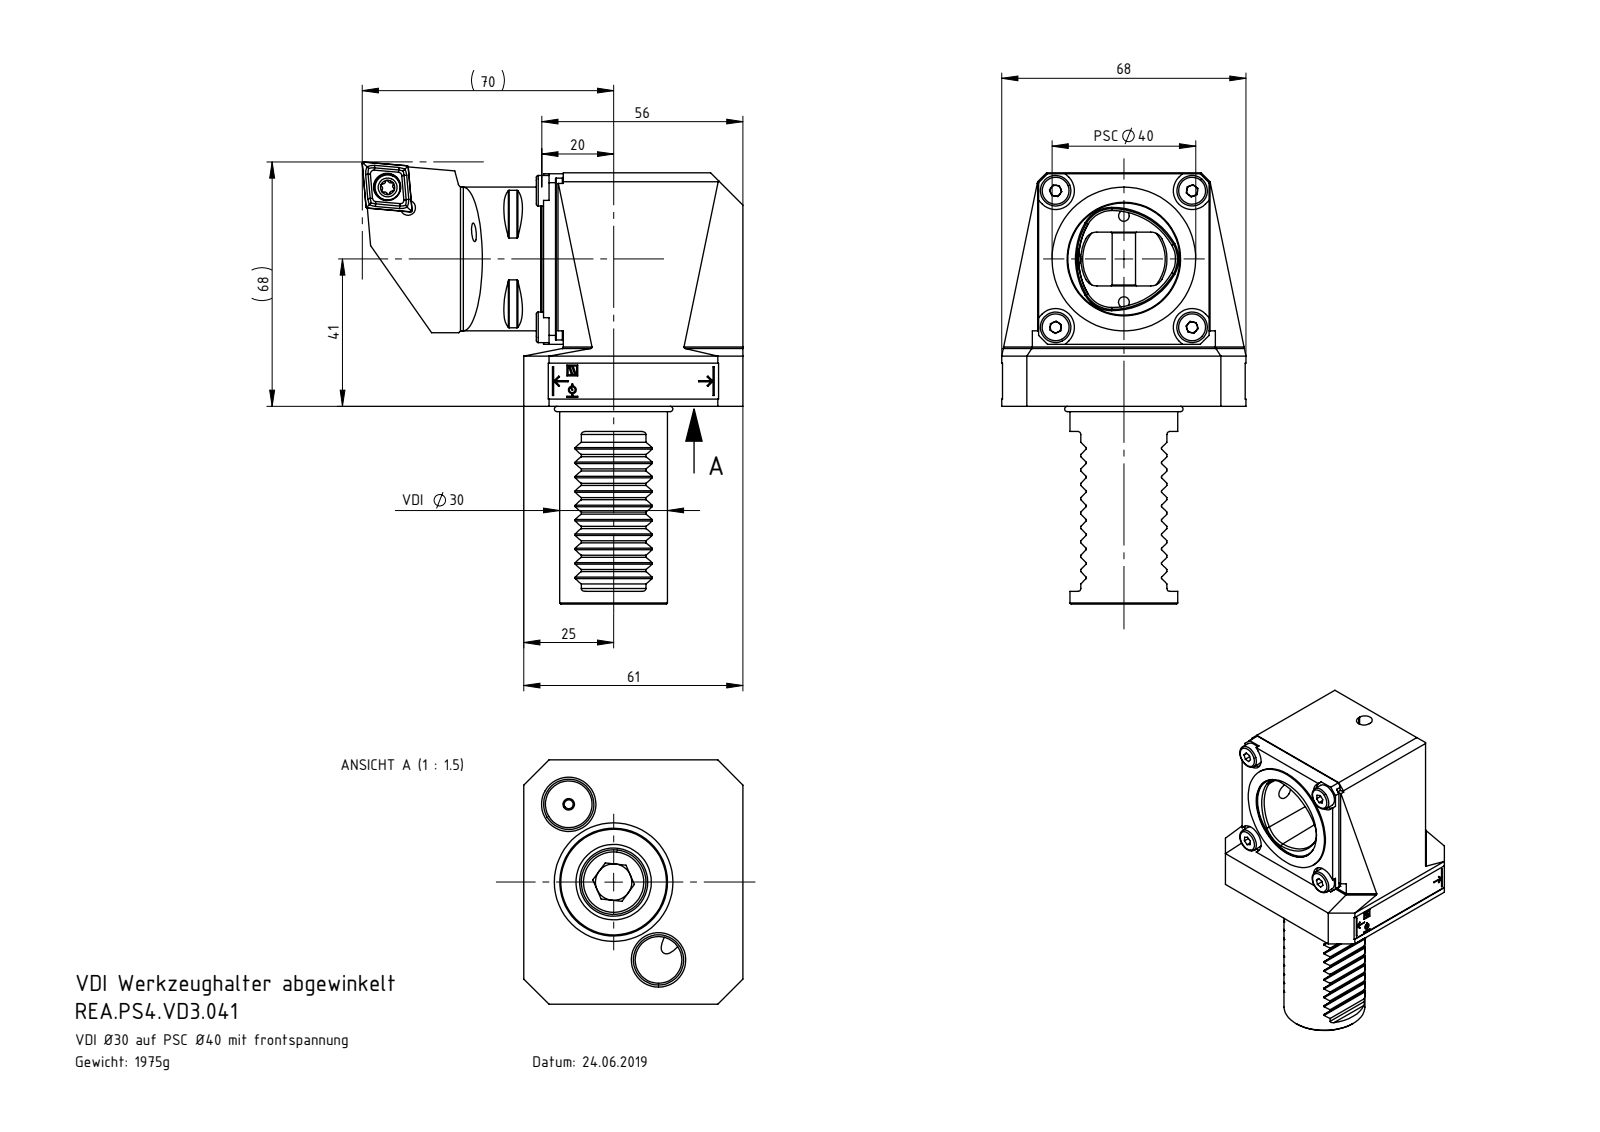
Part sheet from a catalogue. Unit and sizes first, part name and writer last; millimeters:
Units: millimetres
Overall size (bounding box): 120 × 68 × 61
Round holes (diameter × count): ⌀2.5 ×4, ⌀4.2 ×4, ⌀5 ×4, ⌀5.5 ×4, ⌀13 ×3, ⌀3 ×2, ⌀3.3 ×2, ⌀6.8 ×2, ⌀4 ×1, ⌀6 ×1, ⌀7 ×1, ⌀10.2 ×1
Round bosses / shafts (diameter × count): ⌀8.5 ×4, ⌀5 ×4, ⌀6 ×2, ⌀5.5 ×2, ⌀3 ×2, ⌀40 ×1, ⌀39.7 ×1, ⌀37.8 ×1
Partial cylindrical surfaces — rounded edges, fillets, slot ends (radius × count): R0.3 ×20, R0.4 ×5, R0.8 ×4, R3.5 ×4, R5.25 ×4, R0.2 ×2, R2.75 ×2, R3 ×2
Main face-to-face distances: 65, 3, 5.5, 42, 50, 8, 53, 2.83, 47.5, 2
Hole centre spacings: 20.25, 26.87, 36.36, 38, 12, 12.69, 15.77, 16.49
Volume: 206 818 mm³ · Surface area: 69 411 mm²
Bodies: 25 solids, 931 faces (405 planar, 223 cylindrical, 303 other)
Part name (STEP PRODUCT): DIN 7984 - M5 x 16; VD4-ER1.014.010; DIN 6325_ø2.5x8_2x6; ISO 4762 - M12 x 60 (+8 more)
STEP written by: SolidWorks 2022 (AUTOMOTIVE_DESIGN)
